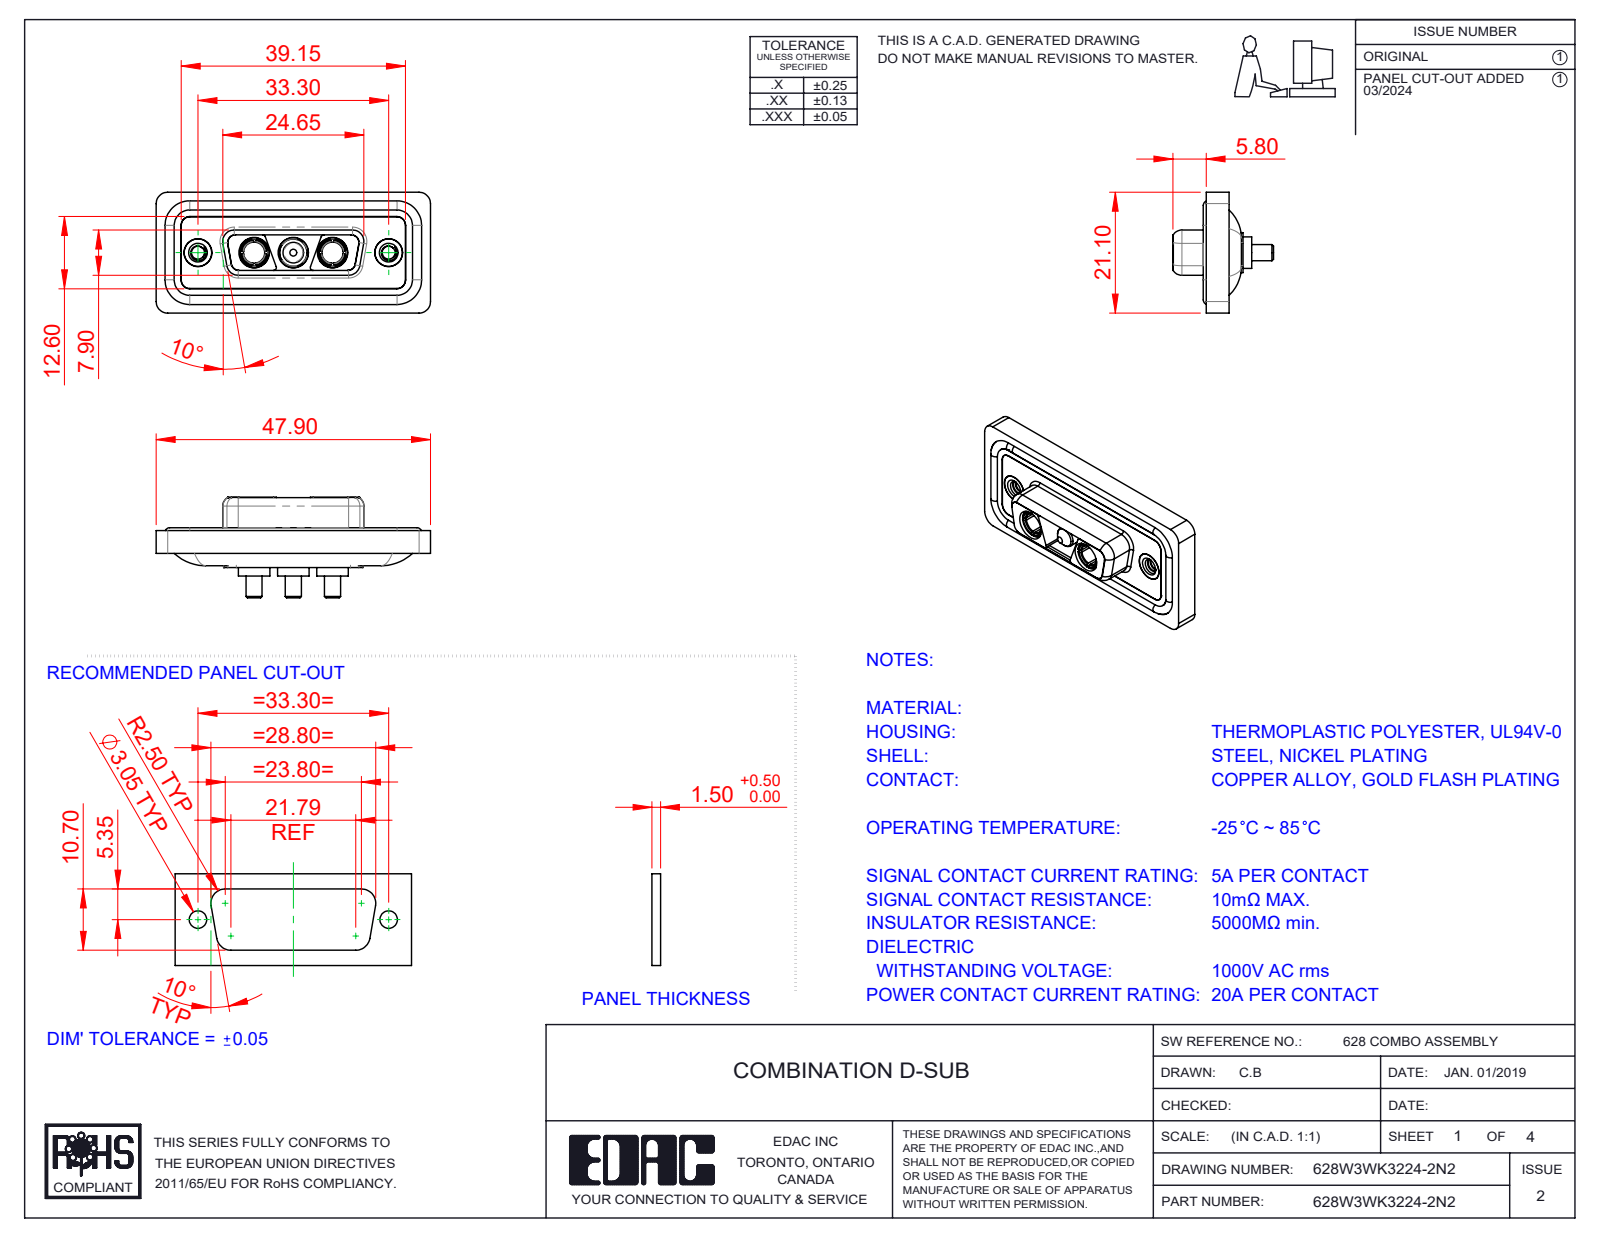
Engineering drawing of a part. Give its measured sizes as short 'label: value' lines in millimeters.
name: Power Socket_20A S; 628Combo Threaded Rivet_2; Power Pin_20A S; 628Combo Waterproof Housing_15 Contacts (+4 more)
written by: SolidWorks 2023 (CONFIG_CONTROL_DESIGN)
unit: mm
bodies: 13 solids, 583 faces (178 planar, 258 cylindrical, 147 other)
size: 47.9 × 21.1 × 17.55
volume: 5 878 mm³; area: 9 505 mm²
holes: 5× ⌀4.85, 3× ⌀5.3, 2× ⌀2.26, 2× ⌀3.7, 2× ⌀4, 2× ⌀4.05, 2× ⌀5
bosses: 4× ⌀1.6, 3× ⌀5.5, 3× ⌀5.2, 3× ⌀4.75, 3× ⌀3.75, 3× ⌀2.8, 2× ⌀4.96, 2× ⌀4.95
rounds: 22× R1.5, 20× R2, 12× R1.35, 8× R0.5, 8× R1.6, 4× R0.25, 4× R0.6, 4× R0.65
face distances: 0.4, 1.6, 1.8, 0.5, 1.1, 2.9, 5.65, 7.05, 1.5, 5.35
hole spacings: 6.85, 9.8, 16.65, 23.5, 13.7, 33.3
